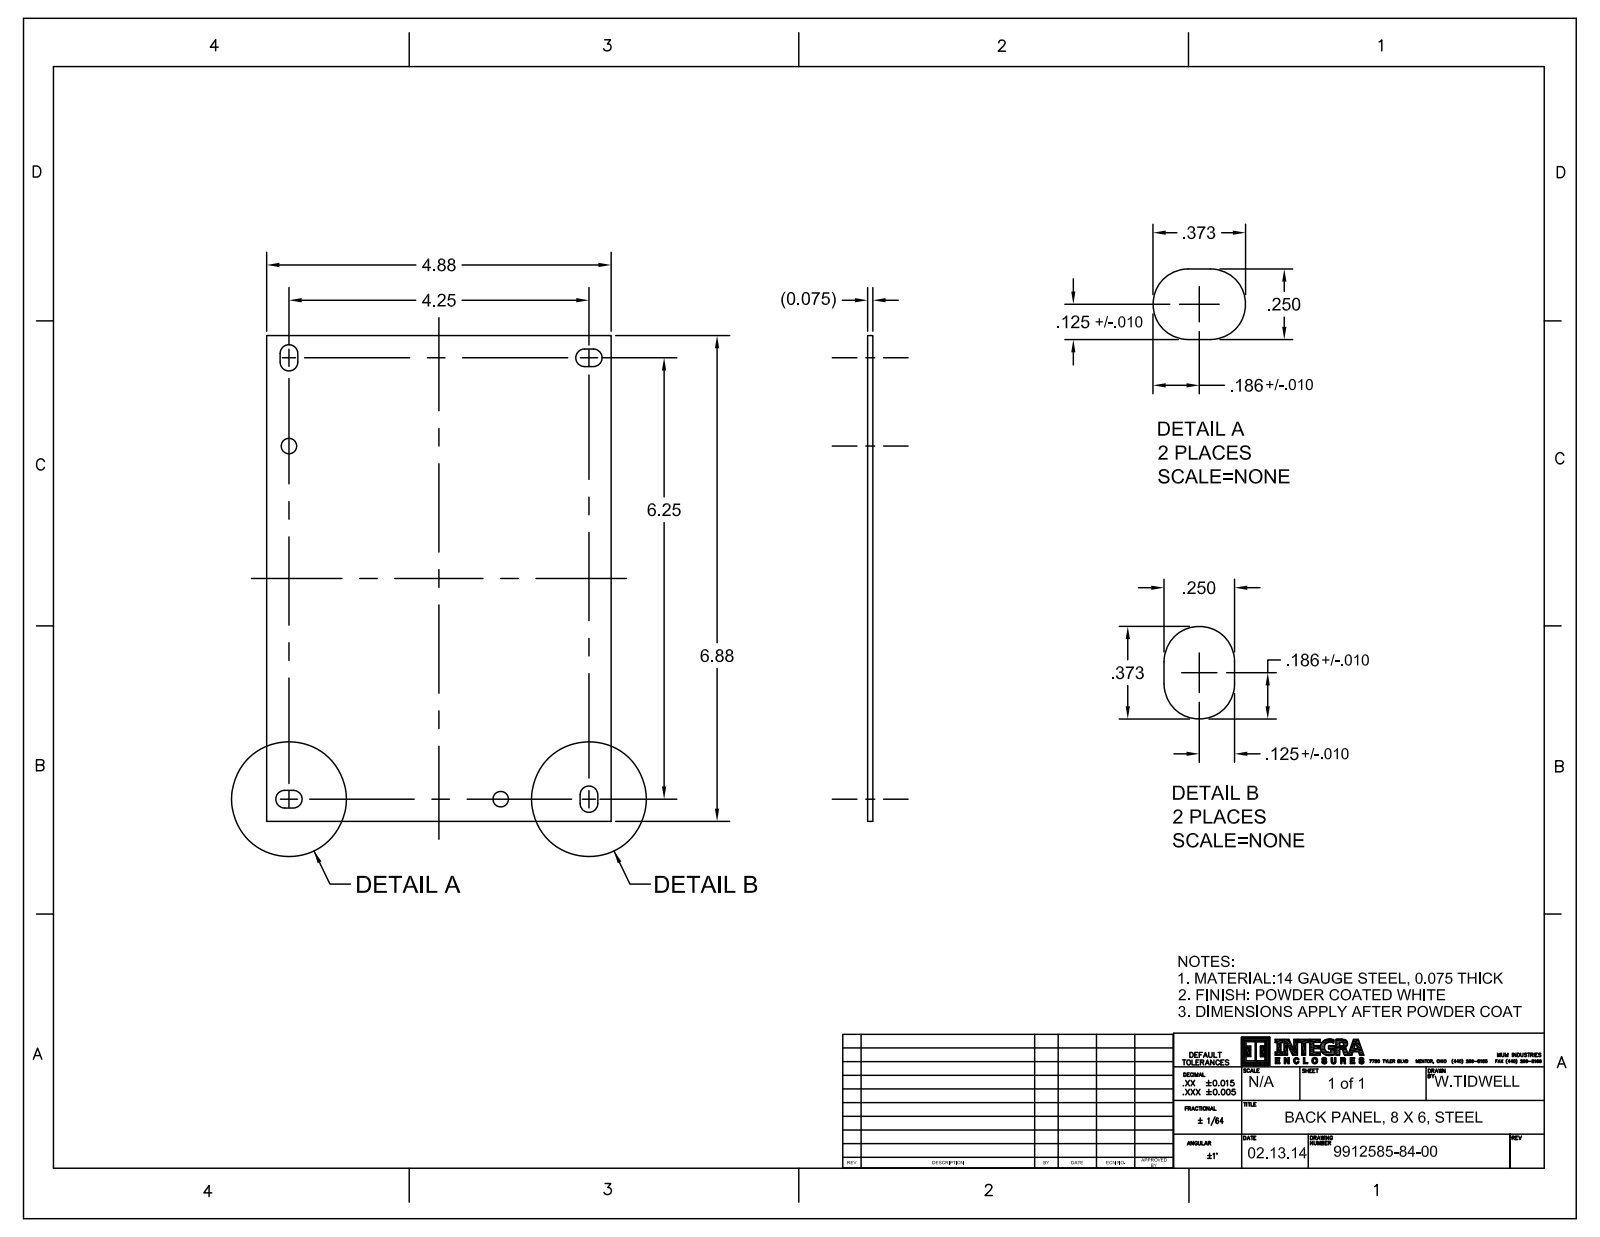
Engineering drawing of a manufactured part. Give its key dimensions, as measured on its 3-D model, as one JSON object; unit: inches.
{"part_name": "9912585-84-00; 9912518-82-10; SBP86_ASM", "step_written_by": "CREO PARAMETRIC BY PTC INC, 2016050 (CONFIG_CONTROL_DESIGN)", "units": "inches", "bodies": {"solids": 5, "faces": 434, "planar": 90, "cylindrical": 272, "other": 72}, "overall_size": [6.88, 4.88, 0.443], "volume_in3": 2.546, "surface_area_in2": 71.05, "round_holes": [[0.219, 2]], "round_bosses_or_shafts": [[0.373, 4], [0.19, 4], [0.149, 4]], "partial_cylinders_radius": [[0.004, 48], [0.125, 8]], "face_to_face_distances": [0.075, 4.88, 6.88, 0.238, 0.313, 0.19, 0.44, 0.25, 4.233, 6.225], "hole_center_spacings": [5.831]}
